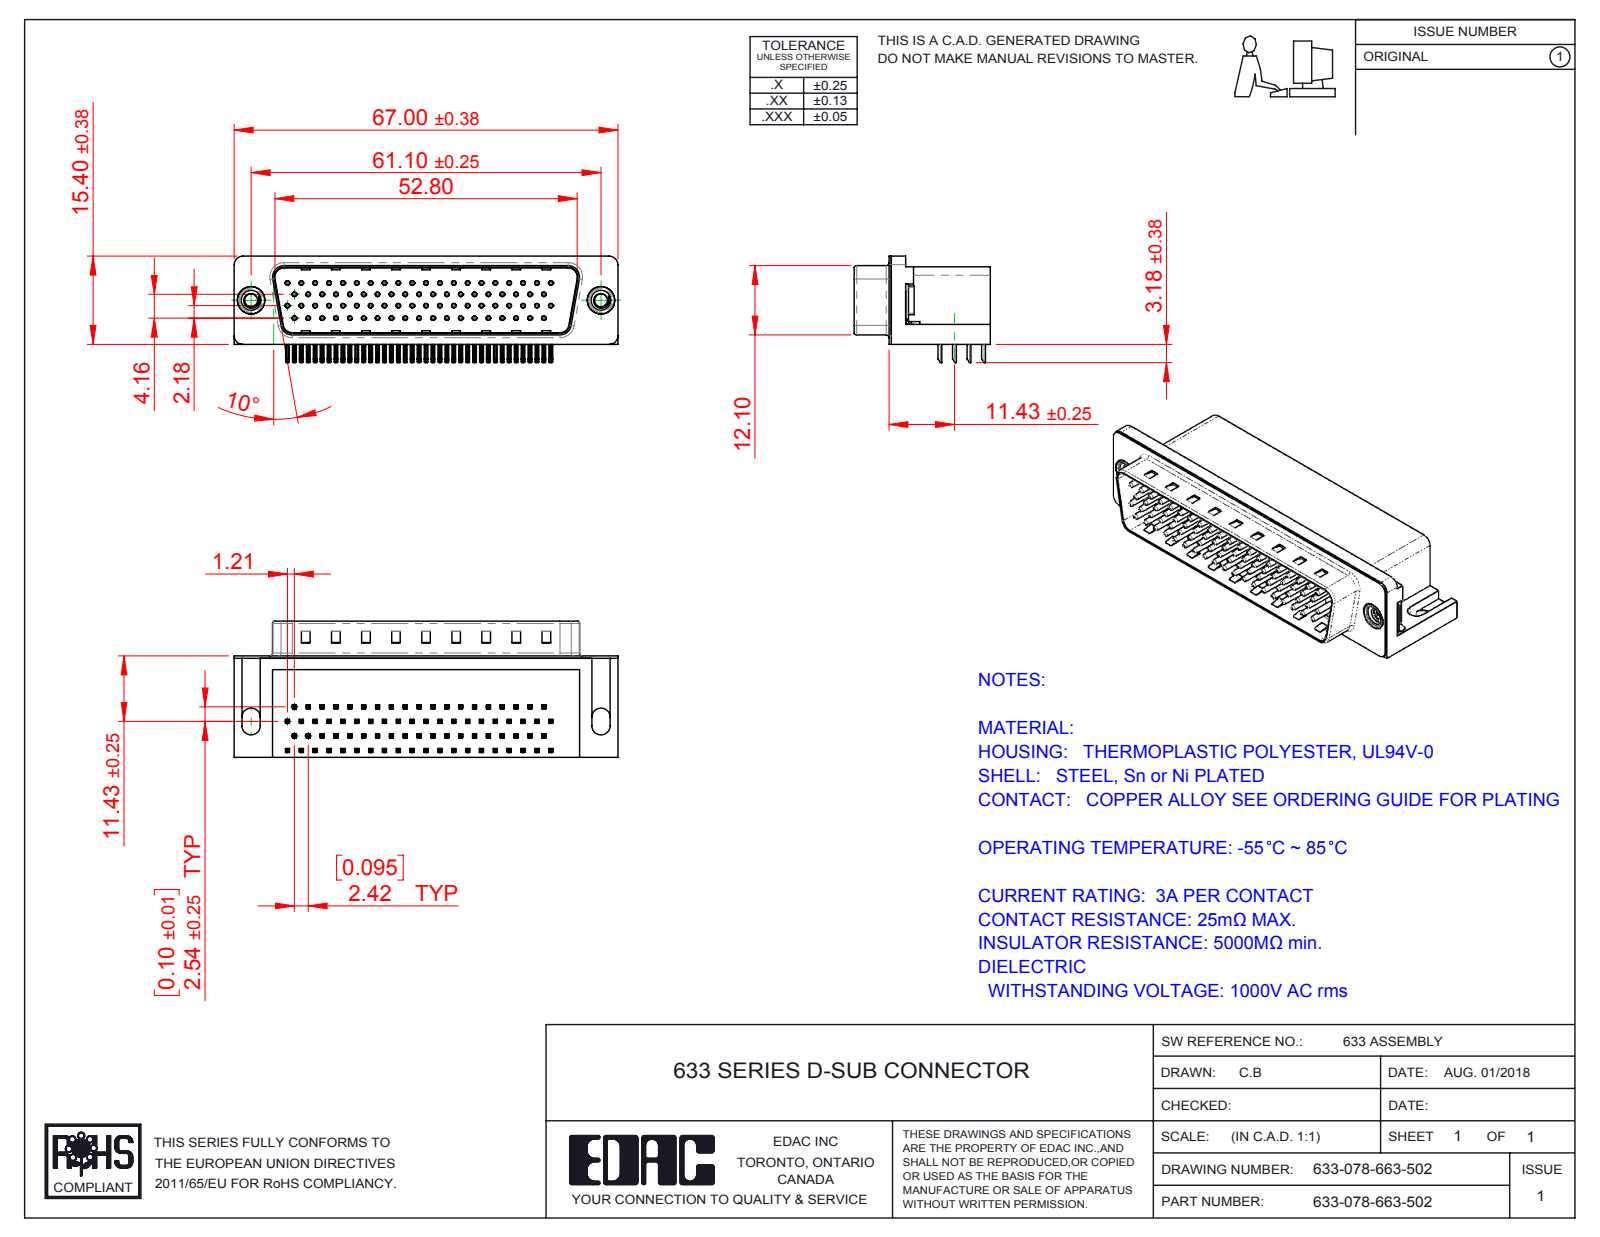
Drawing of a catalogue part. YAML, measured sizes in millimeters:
part_name: "633 Housing_78 Contact; 633 Shell_78 Contact; 633 Contact Bottom_78 Contact; 633 Contact Middle_78 Contact (+5 more)"
step_written_by: "SolidWorks 2016 (CONFIG_CONTROL_DESIGN)"
units: millimeters
bodies: {solids: 84, faces: 6270, planar: 3979, cylindrical: 1774, other: 517}
overall_size: [67, 23.8, 18.58]
volume: 14566
surface_area: 16125
round_holes:
  - {diameter: 0.35, count: 78}
  - {diameter: 0.8, count: 78}
  - {diameter: 2.26, count: 2}
  - {diameter: 4, count: 2}
  - {diameter: 4.8, count: 2}
  - {diameter: 5, count: 2}
round_bosses_or_shafts:
  - {diameter: 0.75, count: 78}
  - {diameter: 4.9, count: 2}
  - {diameter: 4.75, count: 2}
  - {diameter: 3.9, count: 2}
partial_cylinders:
  - {radius: 0.25, count: 320}
  - {radius: 0.12, count: 156}
  - {radius: 1, count: 16}
  - {radius: 0.5, count: 9}
  - {radius: 1.6, count: 8}
  - {radius: 1.5, count: 6}
  - {radius: 0.45, count: 4}
  - {radius: 0.9, count: 4}
face_to_face_distances: [0.4, 13.2, 17.3, 11.7, 13.35, 2.05, 13.75, 1.65, 11.9, 1.85]
hole_center_spacings: [2.42, 4.84, 7.26, 9.68, 6.26, 7.13, 12.1, 8.62]
